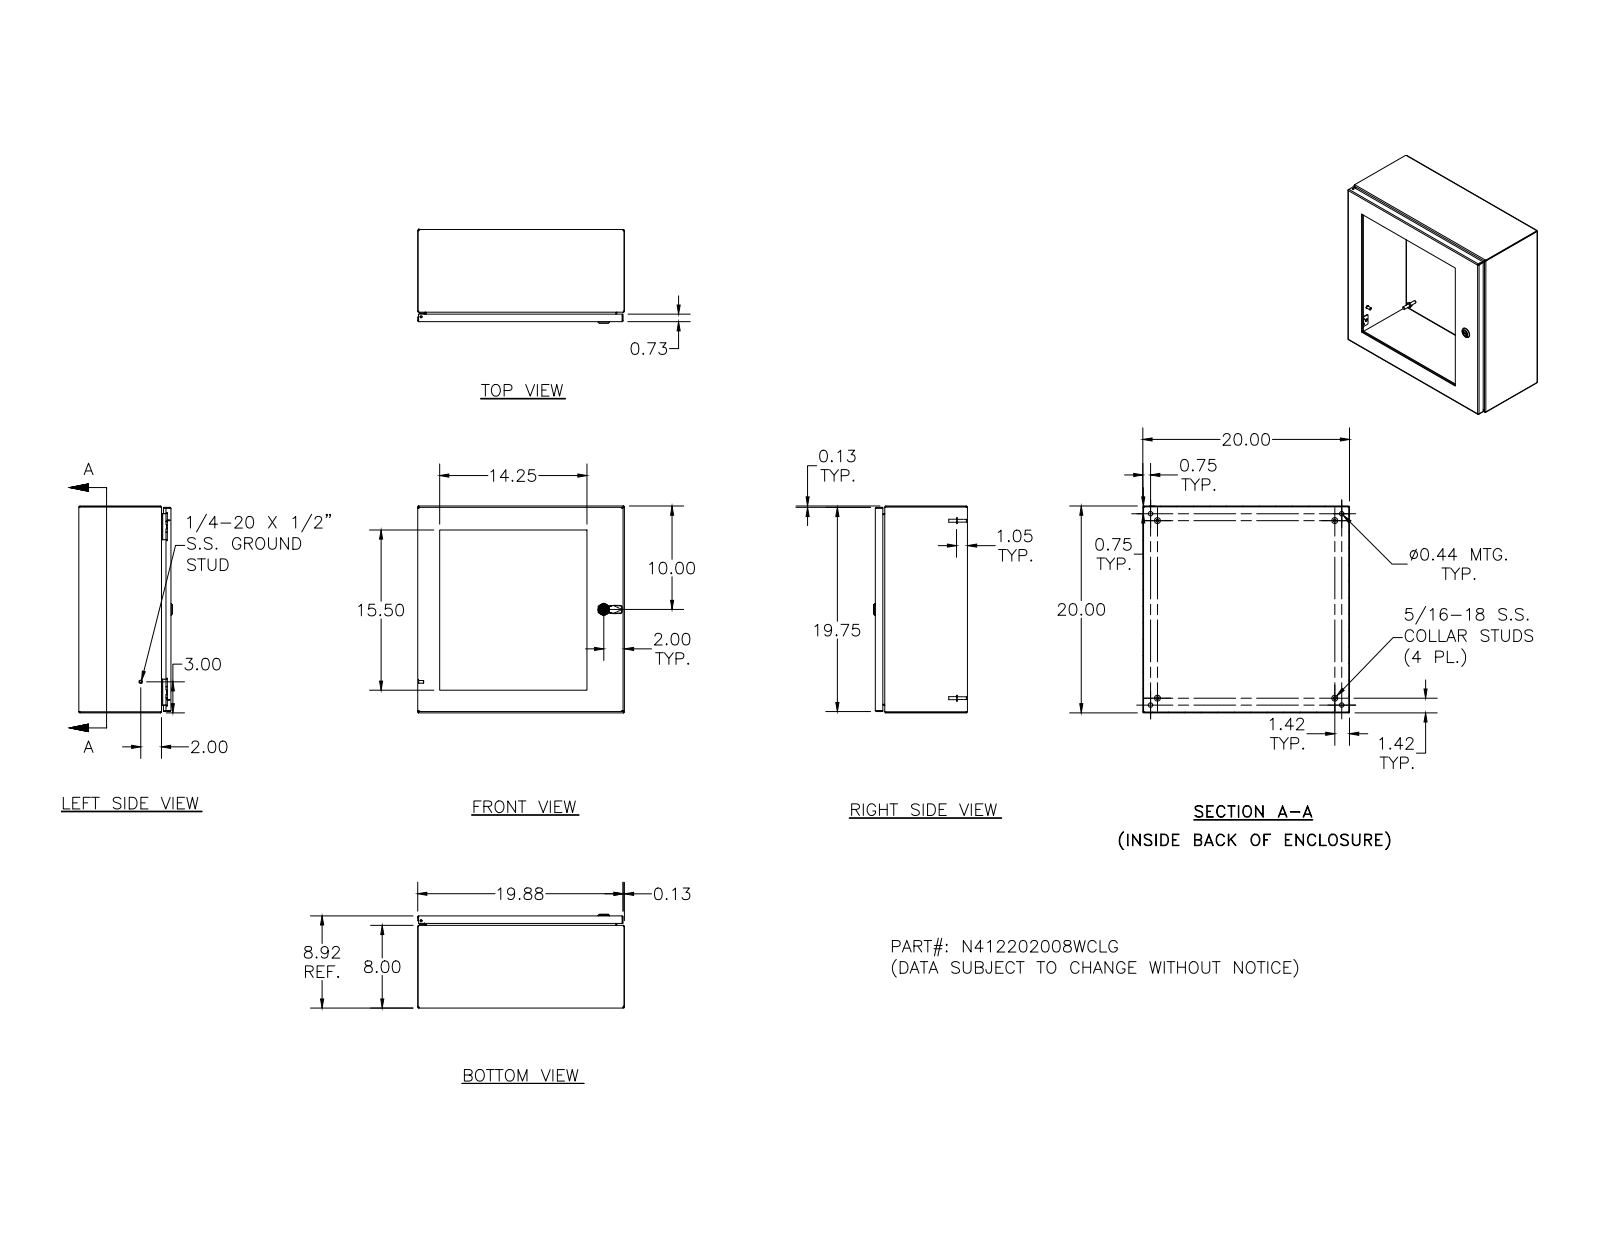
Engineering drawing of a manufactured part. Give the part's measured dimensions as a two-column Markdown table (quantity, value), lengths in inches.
| quantity | value |
| --- | --- |
| part name | N412202008WCLG |
| STEP written by | SolidWorks 2018 (AUTOMOTIVE_DESIGN) |
| units | inches |
| bodies | 69 solids, 2019 faces (753 planar, 617 cylindrical, 649 other) |
| overall size | 20 × 20 × 9.075 |
| volume | 170.6 in³ |
| surface area | 3 465 in² |
| round holes (diameter × count) | 0.156 × 18, 0.281 × 16, 0.188 × 5, 0.093 × 4, 0.152 × 4, 0.167 × 4, 0.172 × 4, 0.437 × 4, 0.187 × 1, 0.197 × 1, 0.315 × 1, 0.394 × 1 |
| round bosses / shafts (diameter × count) | 0.337 × 16, 0.19 × 16, 0.25 × 10, 0.563 × 4, 0.36 × 4, 0.32 × 4, 0.3 × 4, 0.275 × 4 |
| partial cylindrical surfaces (radius × count) | 0.031 × 34, 0.012 × 30, 0.05 × 26, 0.105 × 24, 0.016 × 18, 0.125 × 16, 0.02 × 13, 0.032 × 8 |
| main face-to-face distances | 0.074, 19.926, 8.843, 8.769, 20, 19.852, 0.25, 8.593, 8.519, 8.917 |
| hole center spacings | 4, 8, 16.008, 16, 17.221, 6.221, 8.585, 10.035 |
